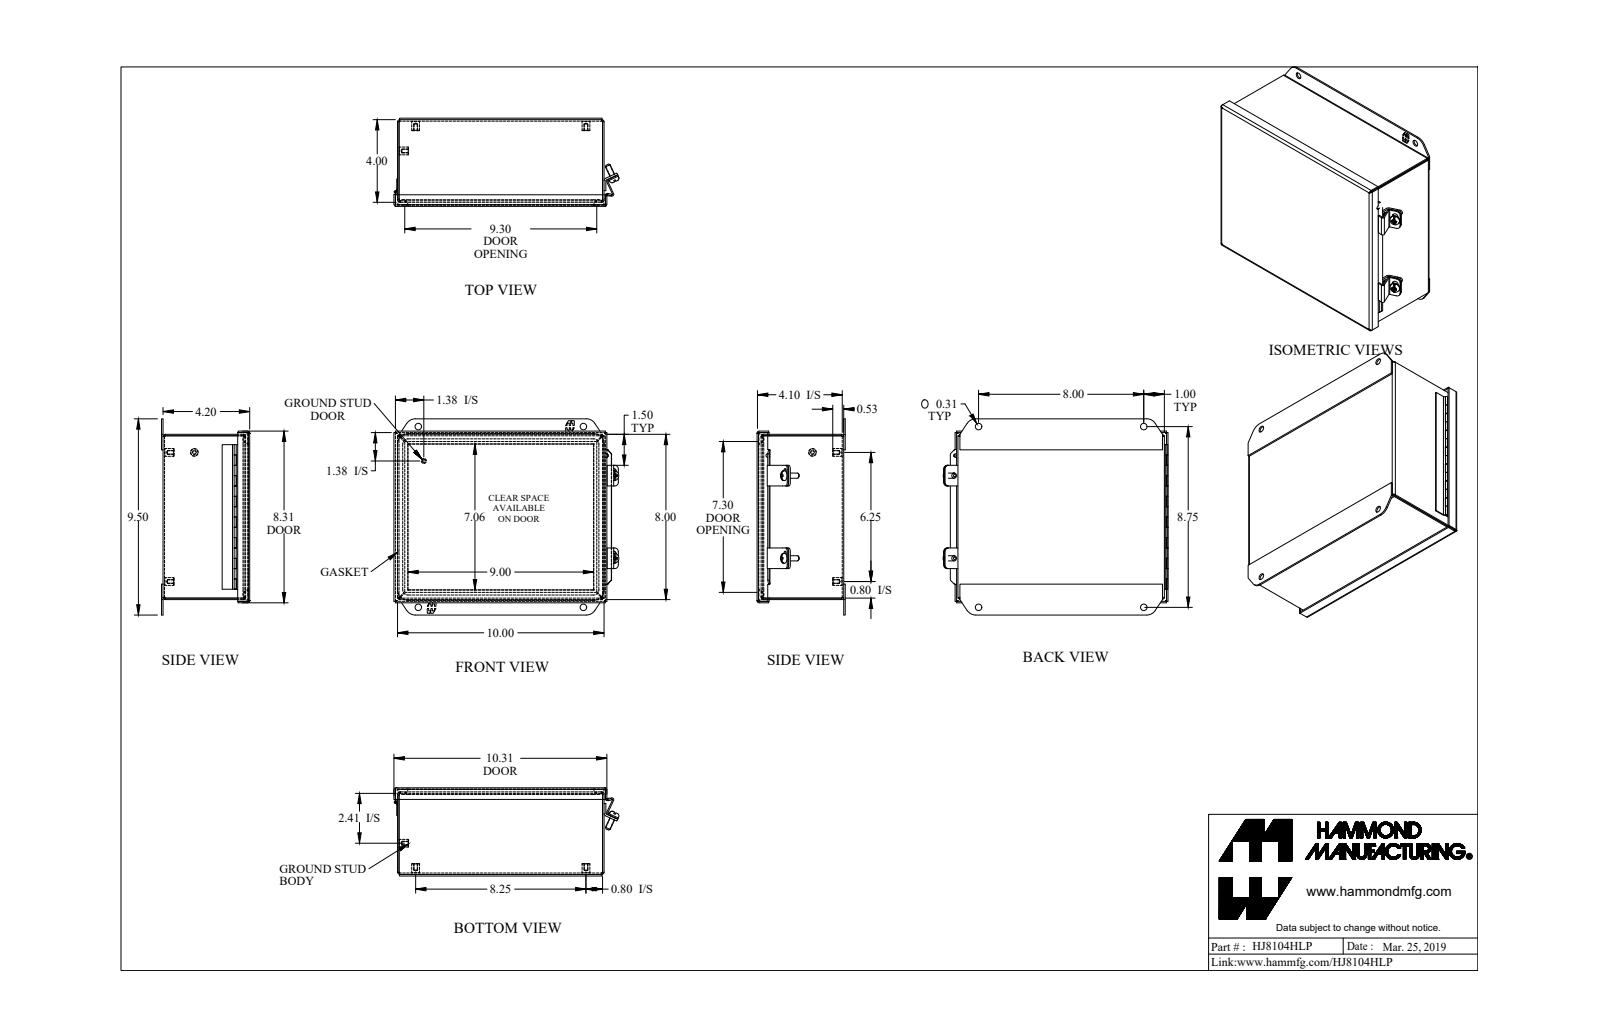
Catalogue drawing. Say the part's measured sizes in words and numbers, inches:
The part is named "HJ8104HLP". Its 3-D file was written by "SolidWorks 2018 (AUTOMOTIVE_DESIGN)". It is 20 solids with 713 faces: 382 planar, 203 cylindrical and 128 other. Overall it measures 10.896 by 9.5 by 4.269 inches. Its volume is 30.2 cubic inches and its surface area 847.6 square inches. Round holes: 5 of diameter 0.156, 4 of diameter 0.313, 2 of diameter 0.213, 1 of diameter 0.05. Round bosses or shafts: 5 of diameter 0.375, 3 of diameter 0.25, 2 of diameter 0.48, 1 of diameter 0.188, 1 of diameter 0.1, 1 of diameter 0.045. Partial cylindrical surfaces (rounded edges, fillets, slot ends): 16 of radius 0.25, 13 of radius 0.036, 13 of radius 0.108, 4 of radius 0.01, 4 of radius 0.141, 4 of radius 0.188, 4 of radius 0.499, 4 of radius 0.5. The main face-to-face distances are 0.072, 4.125, 4.197, 4.053, 7.928, 9.928, 8, 7.856, 10, 9.856. The hole center spacings are 1.256, 7.502, 8.22, 11.057, 6.25, 8, 8.25, 8.75.
